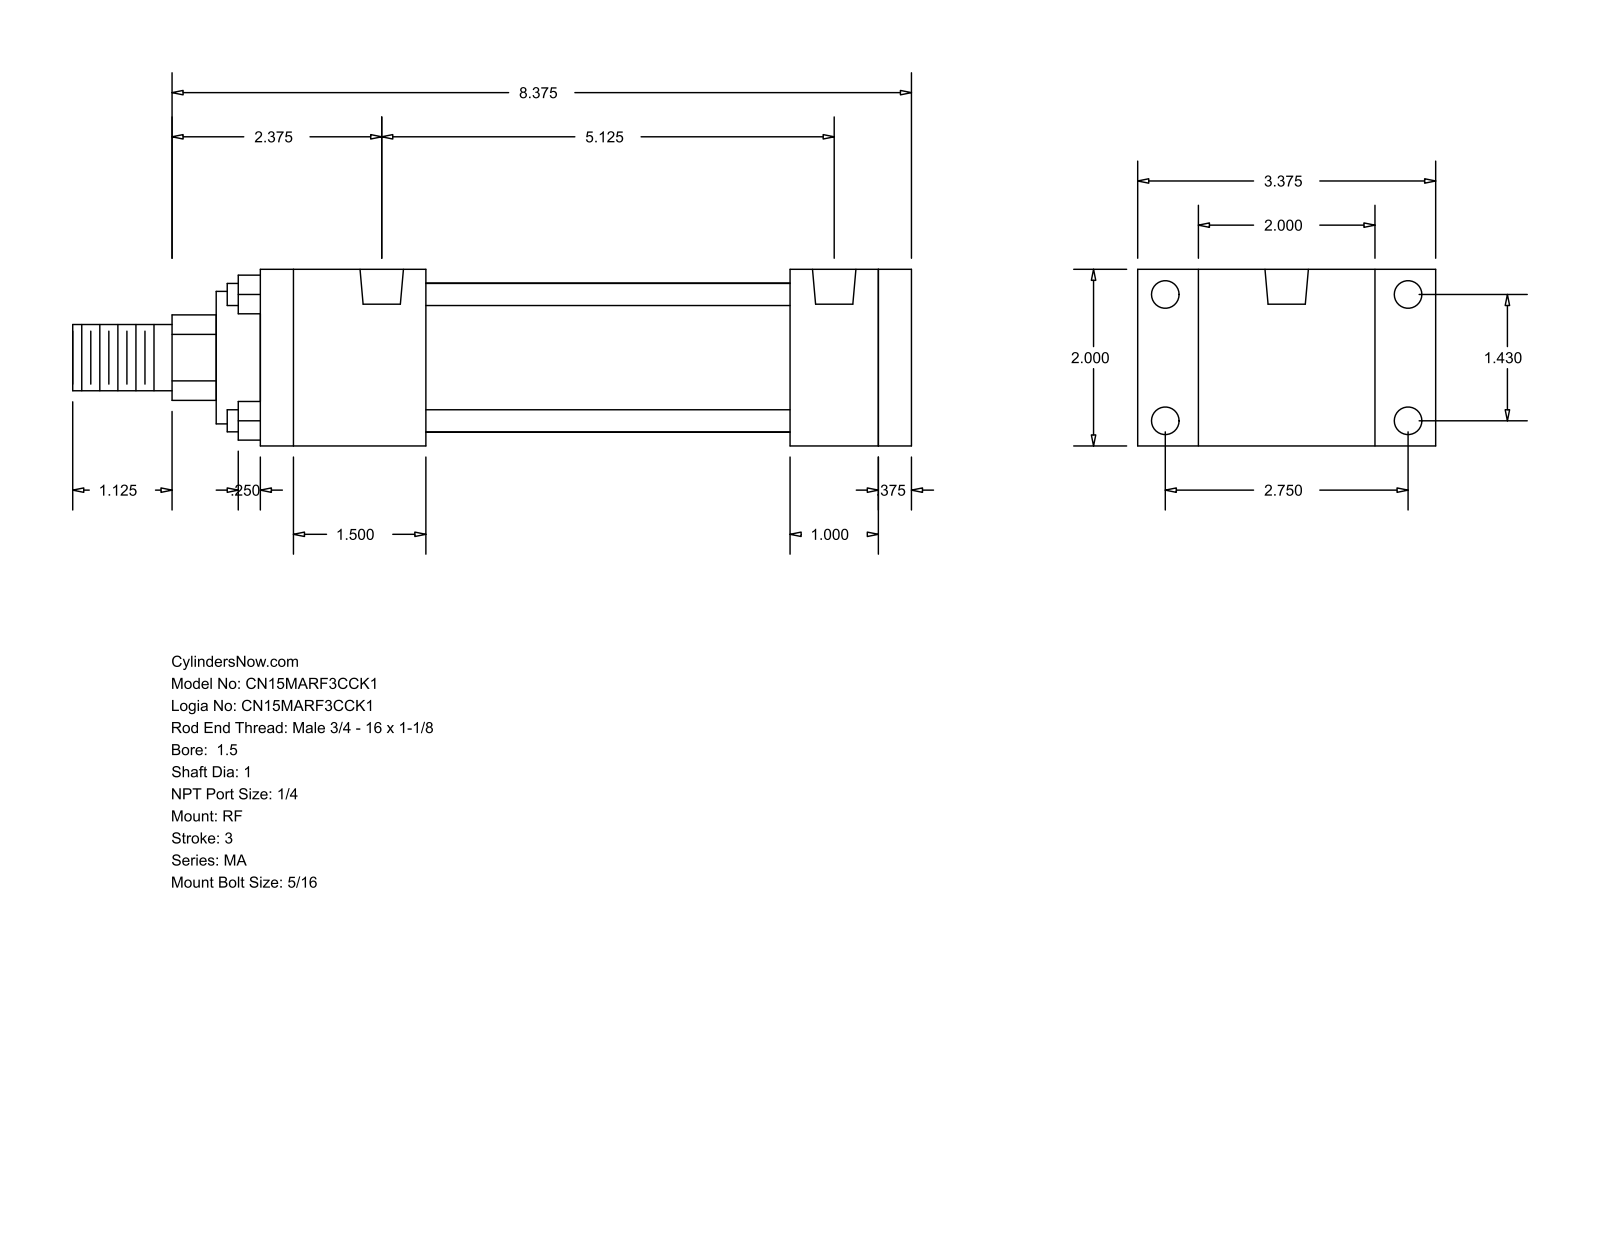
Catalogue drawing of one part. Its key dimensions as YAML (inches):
part_name: "MA_RF__0150_1"
step_written_by: "GSSL Pune (CONFIG_CONTROL_DESIGN)"
units: inches
bodies: {solids: 0, faces: 92, planar: 64, cylindrical: 28, other: 0}
overall_size: [9.5, 3.375, 2]
round_holes:
  - {diameter: 0.313, count: 8}
  - {diameter: 0.492, count: 2}
round_bosses_or_shafts:
  - {diameter: 0.25, count: 4}
  - {diameter: 1.69, count: 1}
  - {diameter: 1.5, count: 1}
  - {diameter: 1, count: 1}
  - {diameter: 0.75, count: 1}
partial_cylinders:
  - {radius: 0.484, count: 1}
face_to_face_distances: [2, 0.375, 7.375, 7, 1, 6, 1.375, 1.875, 4.125, 5.125]
hole_center_spacings: [1.43, 2.75, 3.099, 5.125]
